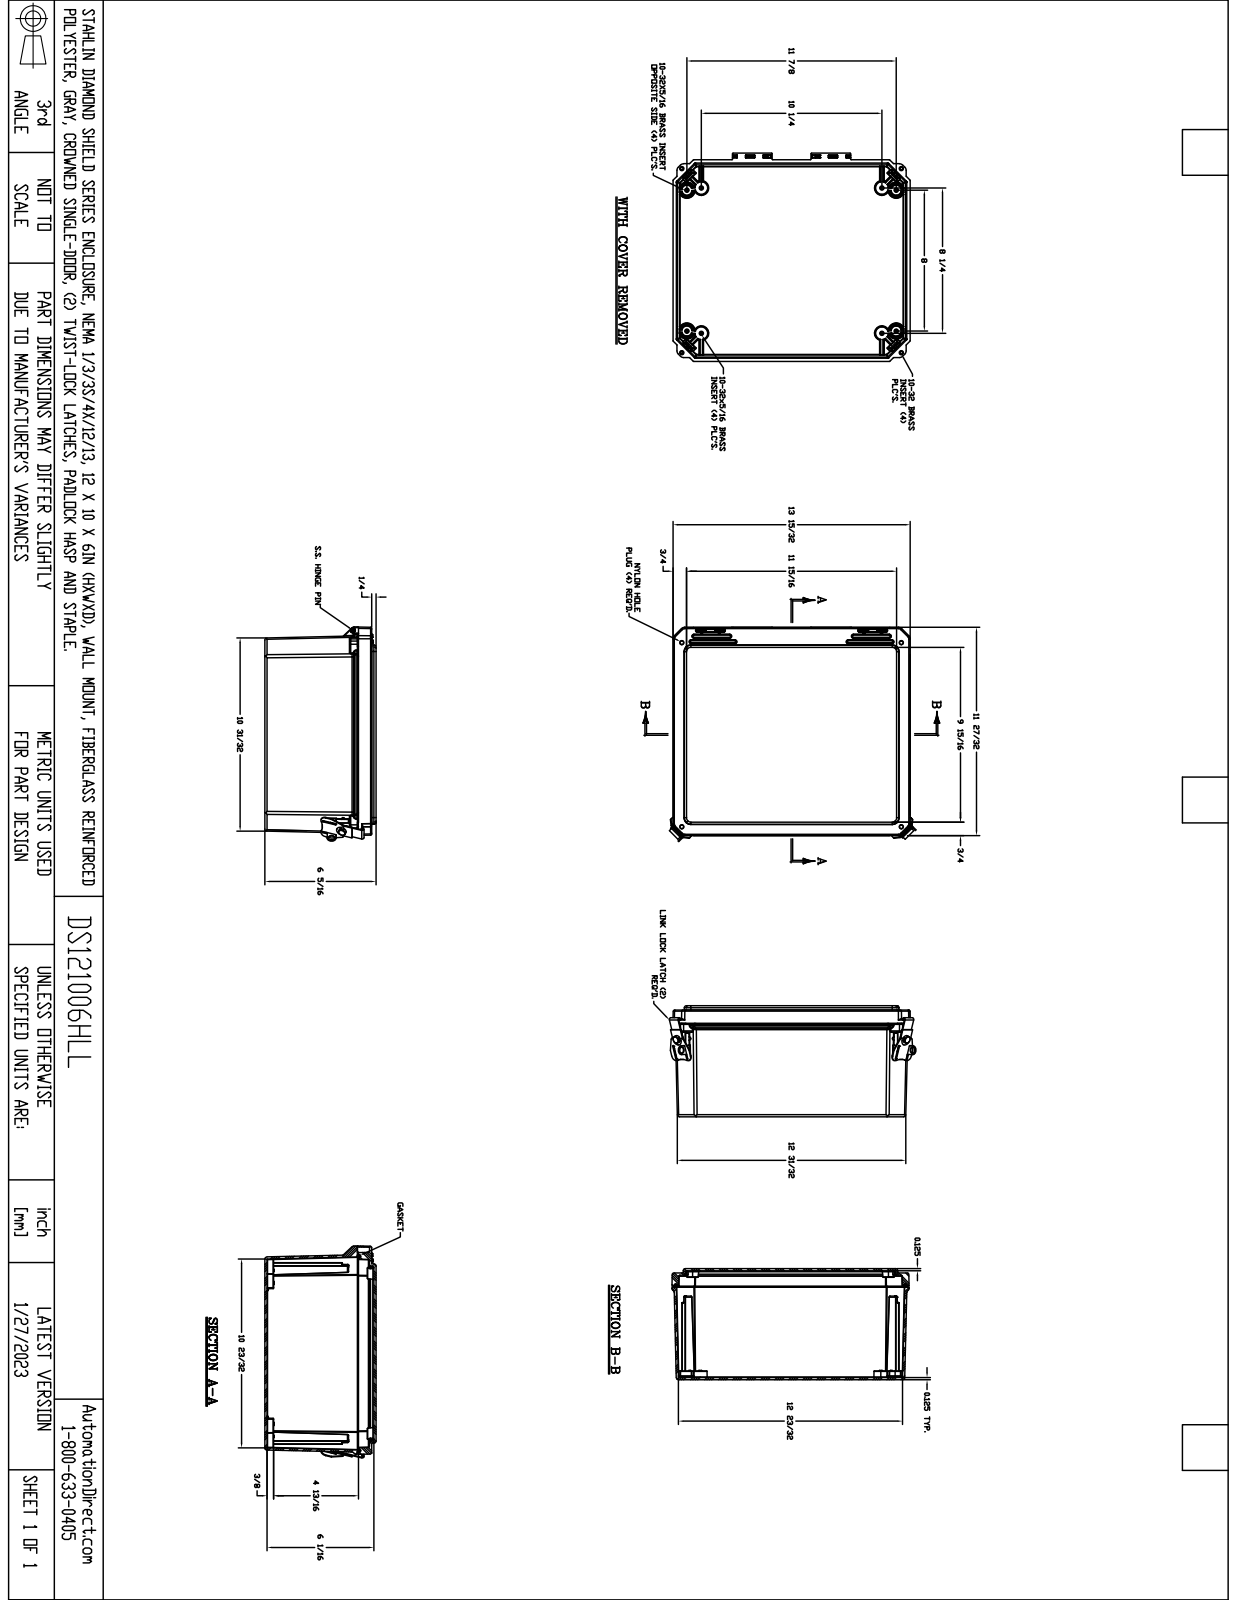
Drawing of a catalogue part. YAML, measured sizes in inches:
part_name: "FR121006HLL"
step_written_by: "SolidWorks 2018 (AUTOMOTIVE_DESIGN)"
units: inches
bodies: {solids: 37, faces: 2258, planar: 765, cylindrical: 892, other: 601}
overall_size: [14.337, 12.27, 6.302]
volume: 93.49
surface_area: 1300
round_holes:
  - {diameter: 0.156, count: 16}
  - {diameter: 0.152, count: 8}
  - {diameter: 0.15, count: 4}
  - {diameter: 0.252, count: 4}
  - {diameter: 0.253, count: 4}
  - {diameter: 0.05, count: 2}
  - {diameter: 0.098, count: 2}
  - {diameter: 0.12, count: 2}
  - {diameter: 0.137, count: 2}
  - {diameter: 0.219, count: 2}
  - {diameter: 0.227, count: 2}
  - {diameter: 0.313, count: 2}
round_bosses_or_shafts:
  - {diameter: 0.246, count: 16}
  - {diameter: 0.87, count: 4}
  - {diameter: 0.209, count: 4}
  - {diameter: 0.6, count: 2}
  - {diameter: 0.435, count: 2}
  - {diameter: 0.2, count: 2}
  - {diameter: 0.135, count: 2}
  - {diameter: 0.05, count: 2}
partial_cylinders:
  - {radius: 0.01, count: 177}
  - {radius: 0.005, count: 80}
  - {radius: 0.02, count: 57}
  - {radius: 0.03, count: 43}
  - {radius: 0.125, count: 34}
  - {radius: 0.039, count: 28}
  - {radius: 0.03, count: 24}
  - {radius: 0.09, count: 24}
face_to_face_distances: [0.125, 6.052, 0.125, 6.302, 6.176, 6.177, 0.139, 0.14, 0.14, 0.25]
hole_center_spacings: [13.727, 14.708, 15.269, 0.824, 1.261, 1.559, 8.165, 9.231]
